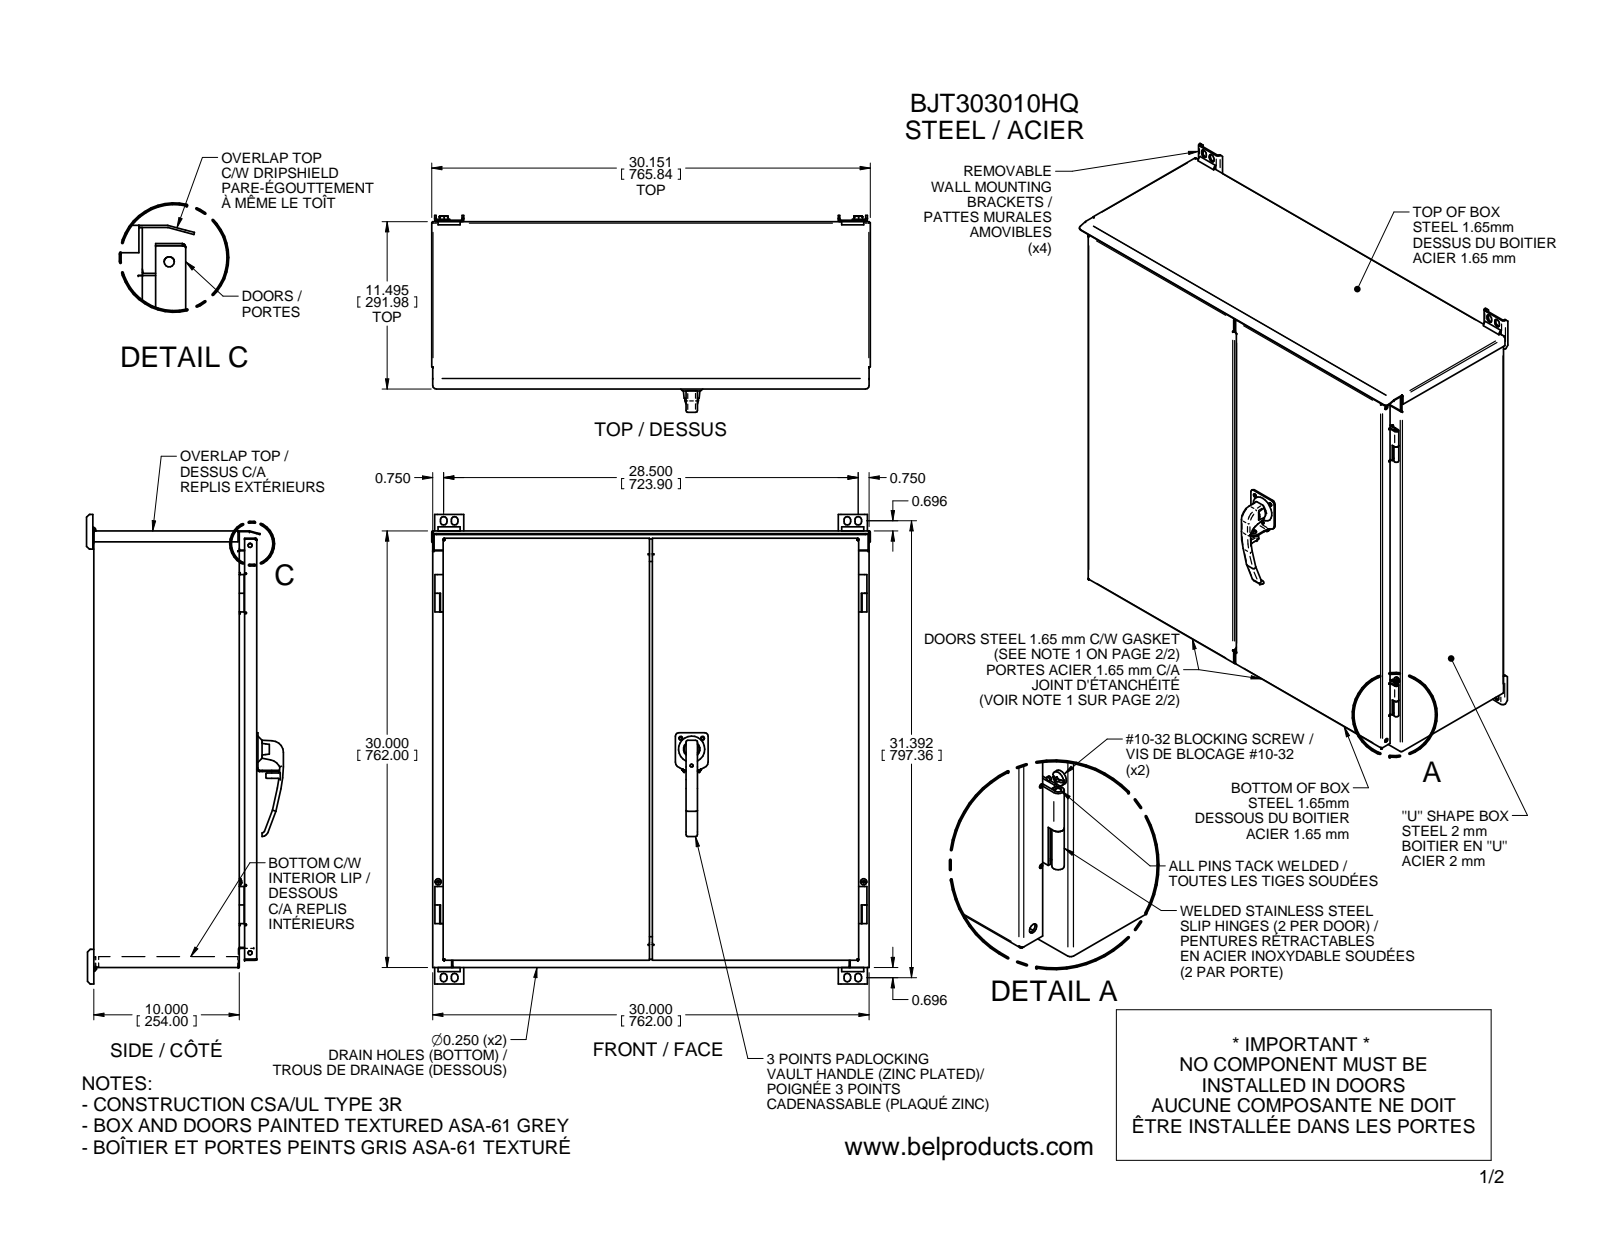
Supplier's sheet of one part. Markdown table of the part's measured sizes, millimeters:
| quantity | value |
| --- | --- |
| part name | BJT303010HQ-A8F3; BJT303010HQ_BOITIER; BJT303010HQ_PORTE_GAUCHE; BJT303010HQ_PORTE_DROITE (+1 more) |
| STEP written by | ST-DEVELOPER v16.7 (AUTOMOTIVE_DESIGN) |
| units | millimeters |
| bodies | 2 solids, 34 faces (26 planar, 4 cylindrical, 4 other) |
| overall size | 753.82 × 12 × 10.87 |
| volume | 813 mm³ |
| surface area | 906 mm² |
| round bosses / shafts (diameter × count) | 10.87 × 2, 4.8 × 2 |
| main face-to-face distances | 7.92, 1.9, 1.52, 9.44, 0.42, 1.1, 9.02, 520.81, 3.1, 529.72 |
